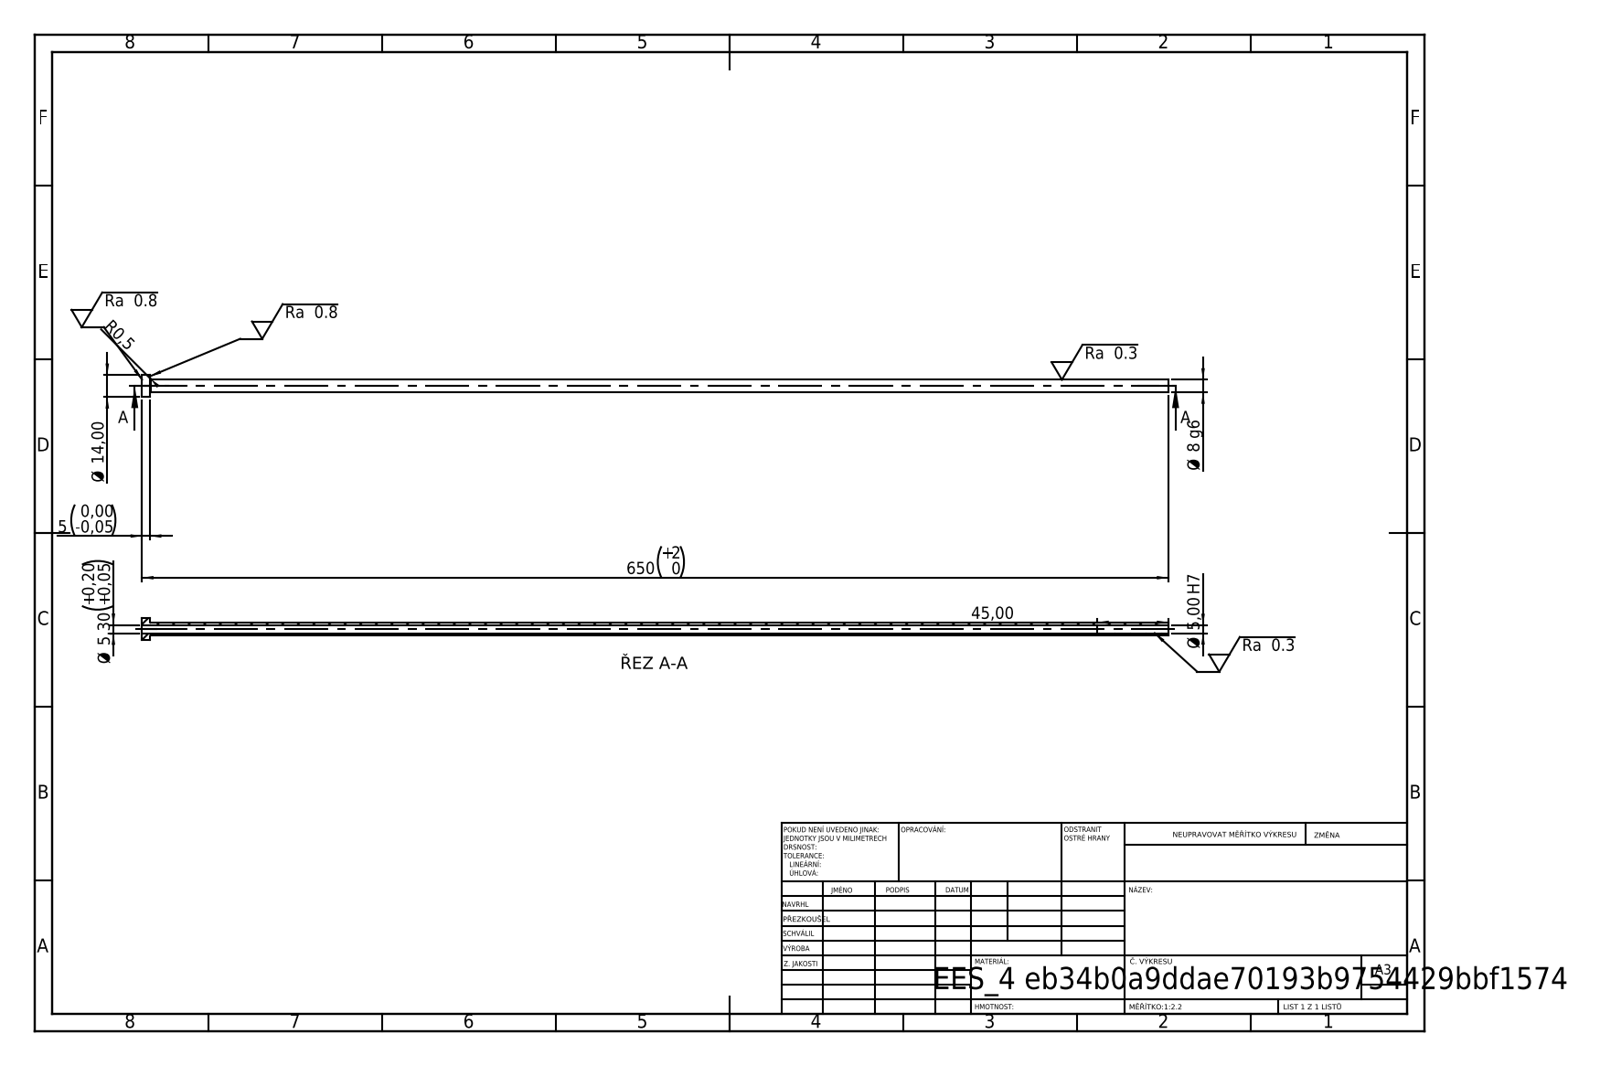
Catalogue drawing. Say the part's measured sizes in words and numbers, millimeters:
Its 3-D file was written by "SolidWorks 2019 (CONFIG_CONTROL_DESIGN)". It is 1 solid with 14 faces: 4 planar, 8 cylindrical and 2 other. Overall it measures 650 by 14 by 14 millimeters. Its volume is 18 961 cubic millimeters and its surface area 27 474 square millimeters. Round holes: 1 of diameter 5, 1 of diameter 5.3. Round bosses or shafts: 1 of diameter 14, 1 of diameter 8. The main face-to-face distances are 5, 650, 645, 605, 600, 45.
